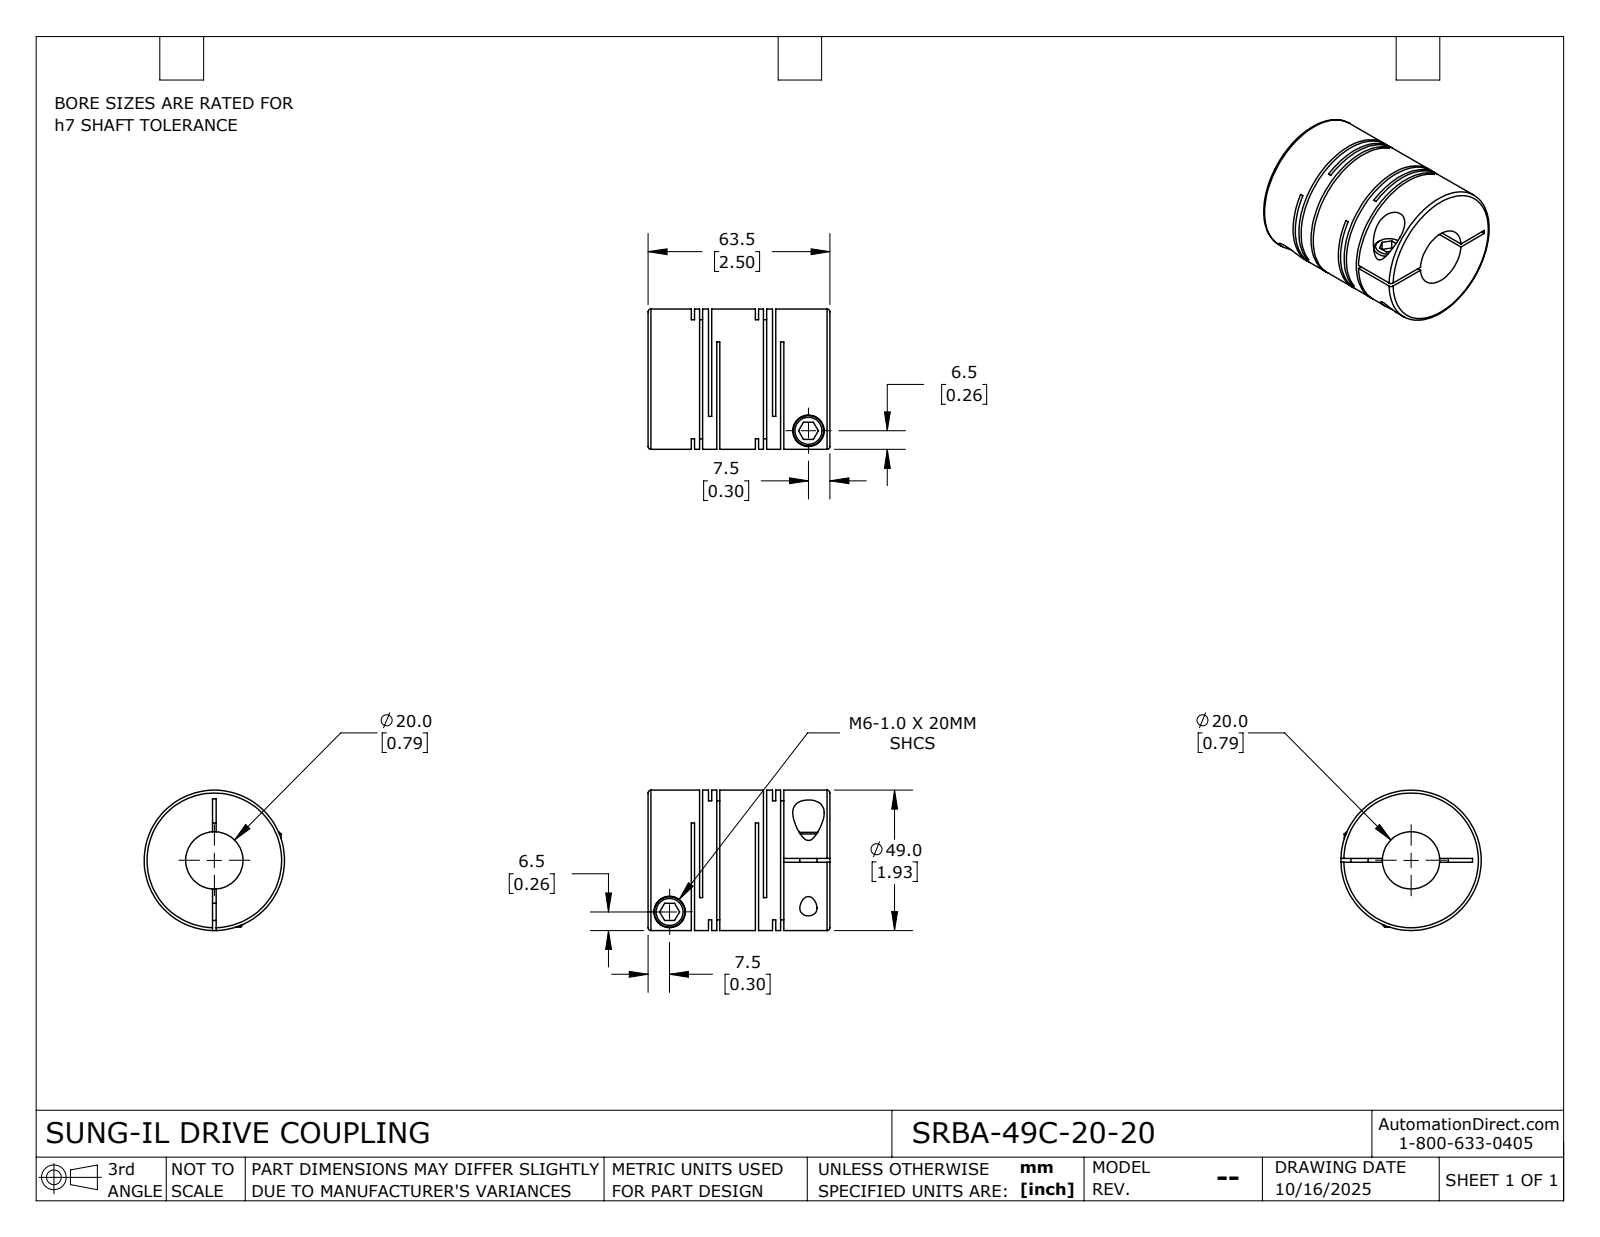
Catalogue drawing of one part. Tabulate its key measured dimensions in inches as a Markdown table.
| quantity | value |
| --- | --- |
| part name | SRBA-49C-20-20 |
| STEP written by | SolidWorks 2024 (CONFIG_CONTROL_DESIGN) |
| units | inches |
| bodies | 1 solid, 115 faces (60 planar, 42 cylindrical, 13 other) |
| overall size | 2.5 × 1.929 × 1.929 |
| volume | 5.261 in³ |
| surface area | 58.86 in² |
| round holes (diameter × count) | 0.236 × 2, 0.433 × 2, 0.787 × 1 |
| round bosses / shafts (diameter × count) | 0.417 × 2, 1.929 × 1 |
| main face-to-face distances | 0.236, 0.043, 0.88, 0.112, 0.837, 0.124, 0.069, 0.193, 0.768, 0.644 |
